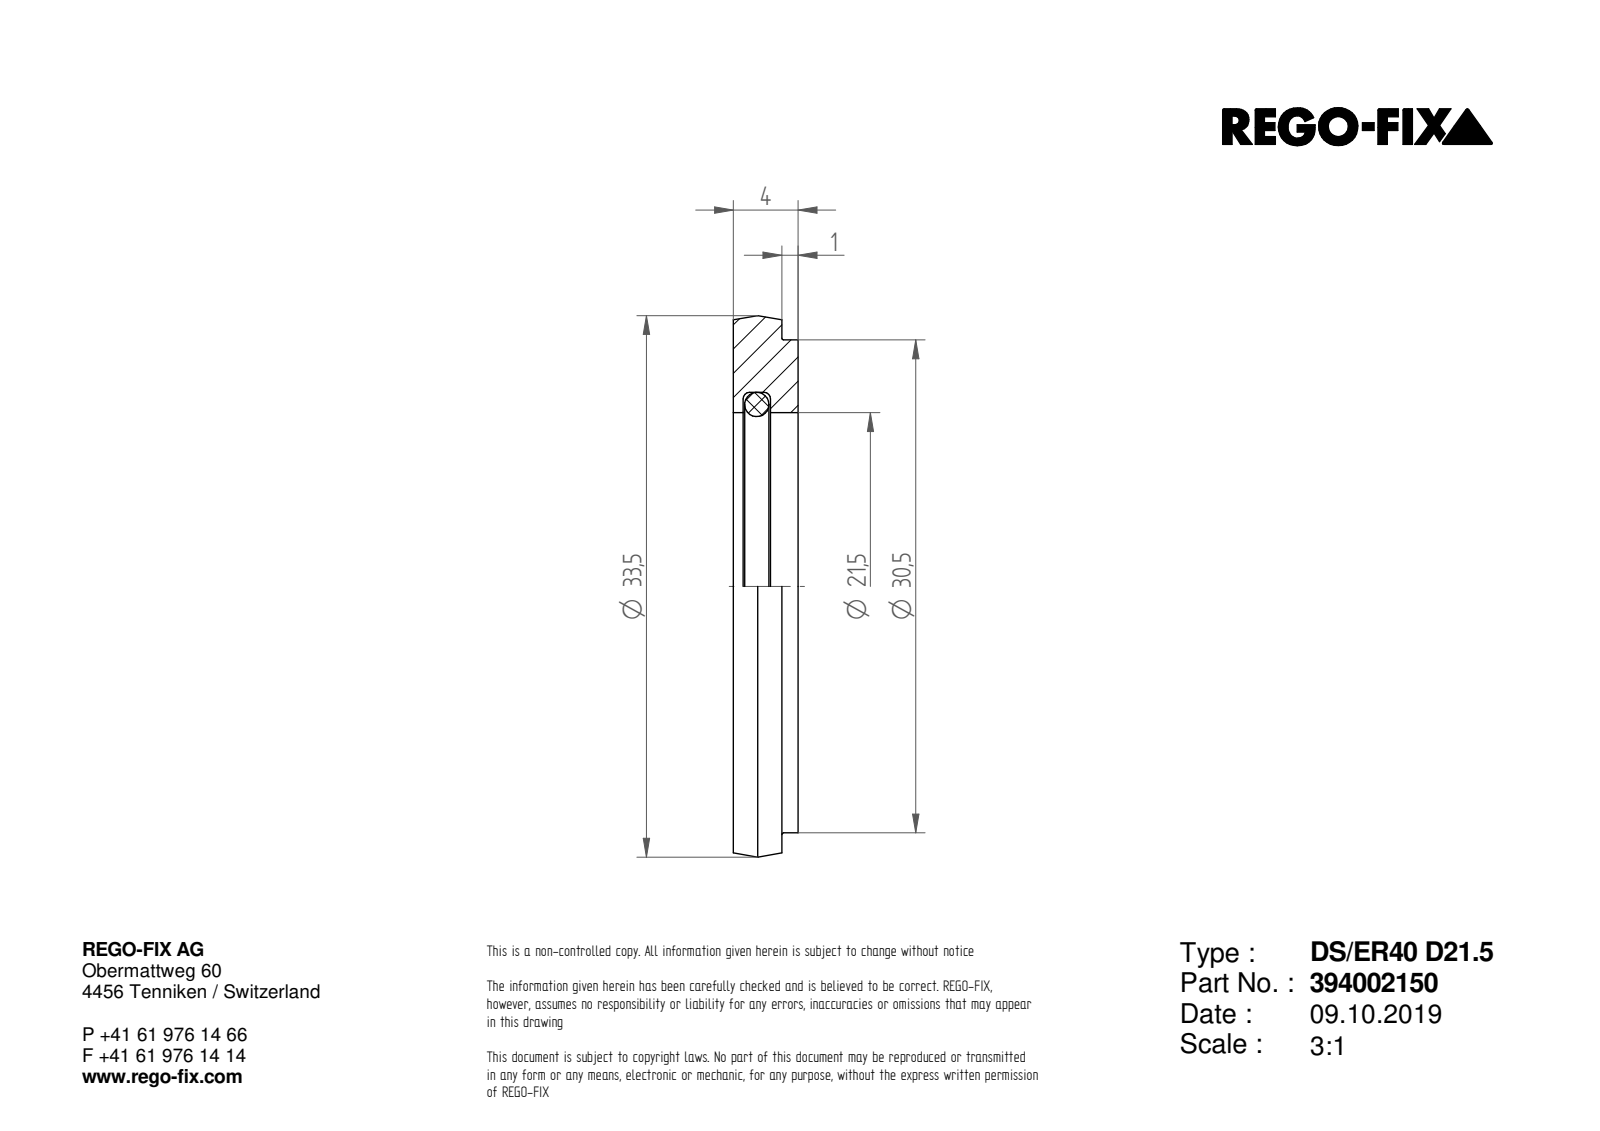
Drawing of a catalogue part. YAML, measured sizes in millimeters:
part_name: "NOCUT"
step_written_by: "SIEMENS PLM Software Solid Edge ST10 (AUTOMOTIVE_DESIGN)"
units: millimeters
bodies: {solids: 1, faces: 7, planar: 3, cylindrical: 3, other: 1}
overall_size: [33.5, 33.5, 4]
volume: 1923
surface_area: 1714
round_holes:
  - {diameter: 21.5, count: 1}
round_bosses_or_shafts:
  - {diameter: 33.5, count: 1}
  - {diameter: 30.5, count: 1}
face_to_face_distances: [4, 1, 3]
